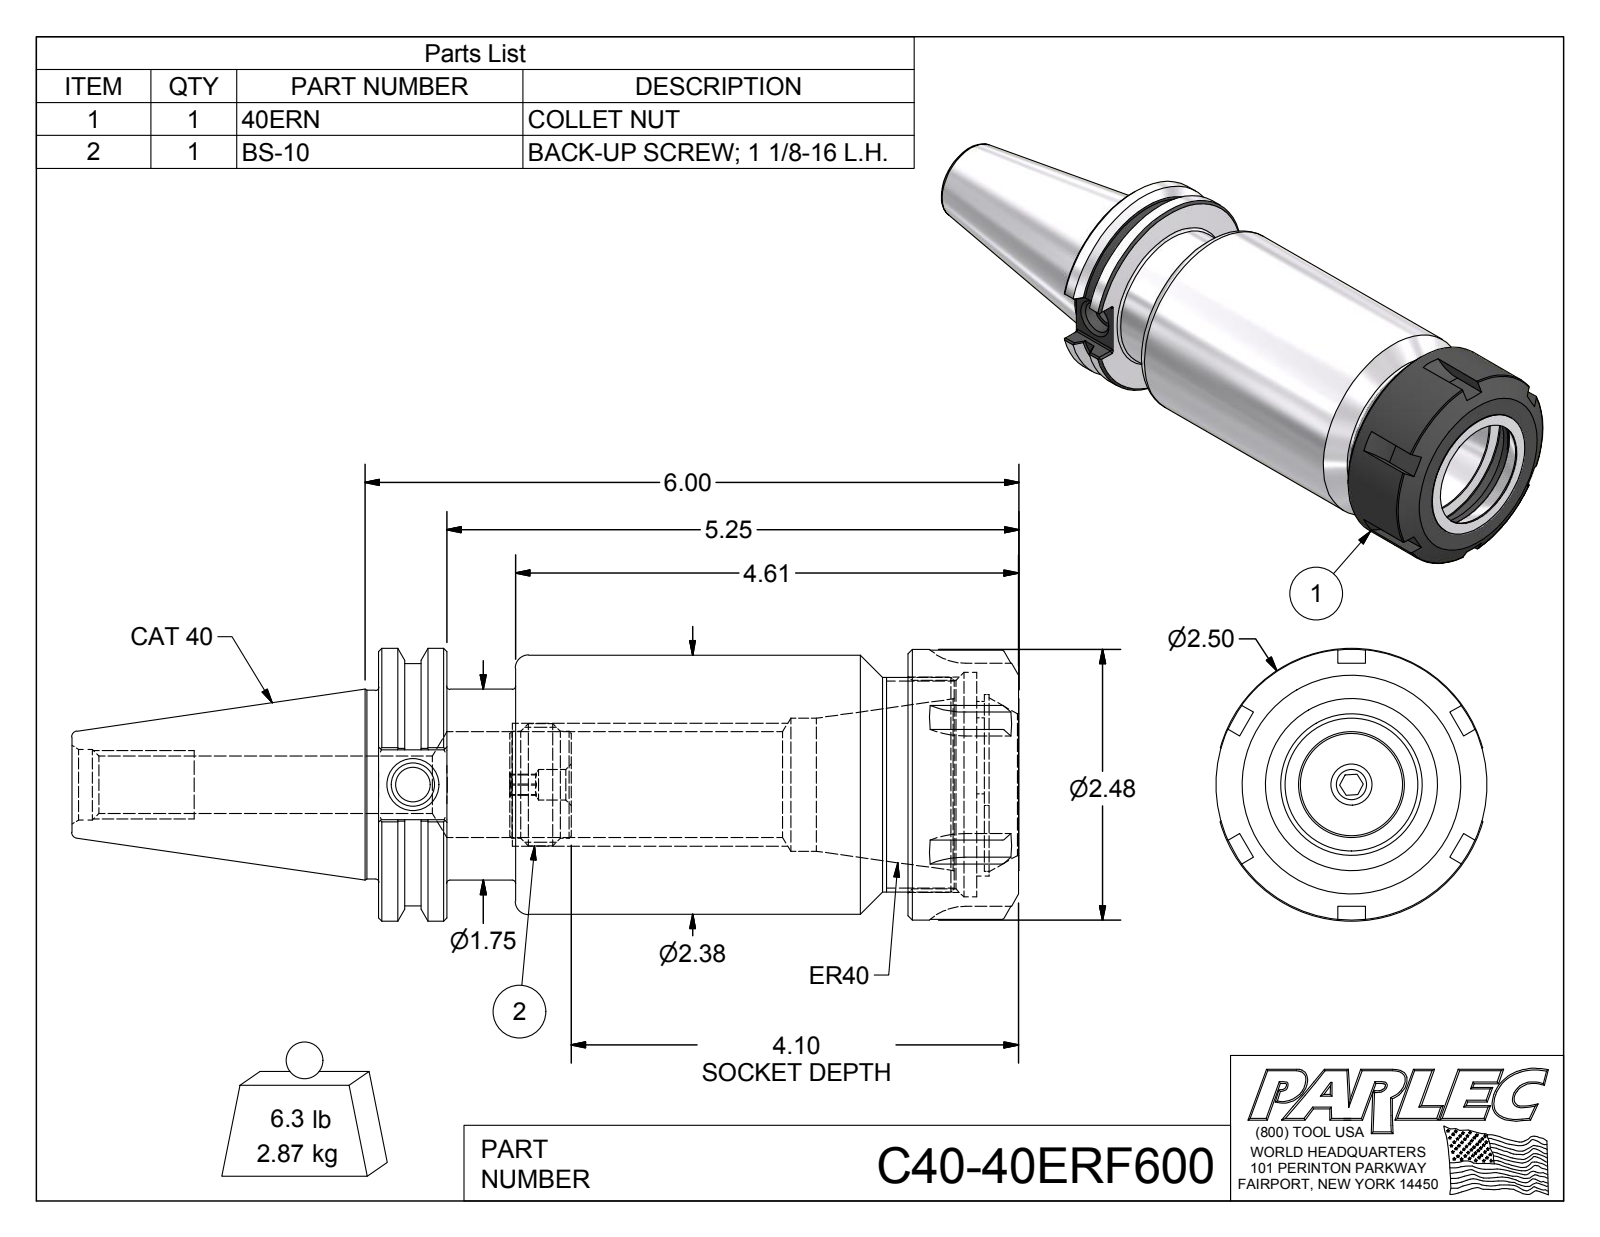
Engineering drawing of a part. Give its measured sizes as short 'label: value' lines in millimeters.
name: C40-40ER6-1; 40ERN; BS-10; C40-40ERF600
written by: Autodesk Inventor 2016 (AUTOMOTIVE_DESIGN)
unit: mm
bodies: 3 solids, 196 faces (75 planar, 52 cylindrical, 69 other)
size: 220.65 × 63.5 × 63
volume: 367 582 mm³; area: 68 332 mm²
holes: 1× ⌀5.59, 1× ⌀7.11, 1× ⌀8, 1× ⌀10.13, 1× ⌀13.39, 1× ⌀16.46, 1× ⌀24.64, 1× ⌀30.99, 1× ⌀33.02, 1× ⌀41.1, 1× ⌀48.5, 1× ⌀52.25
bosses: 1× ⌀63.5, 1× ⌀63, 1× ⌀60.32, 1× ⌀56.36, 1× ⌀50, 1× ⌀44.45, 1× ⌀43.94, 1× ⌀28.4
rounds: 24× R0.51, 1× R18.5, 1× R21
face distances: 149.23, 15.88, 133.35, 123.2, 107.32, 26.03, 139.33, 123.45, 16.13, 9.9
hole spacings: 2.28
